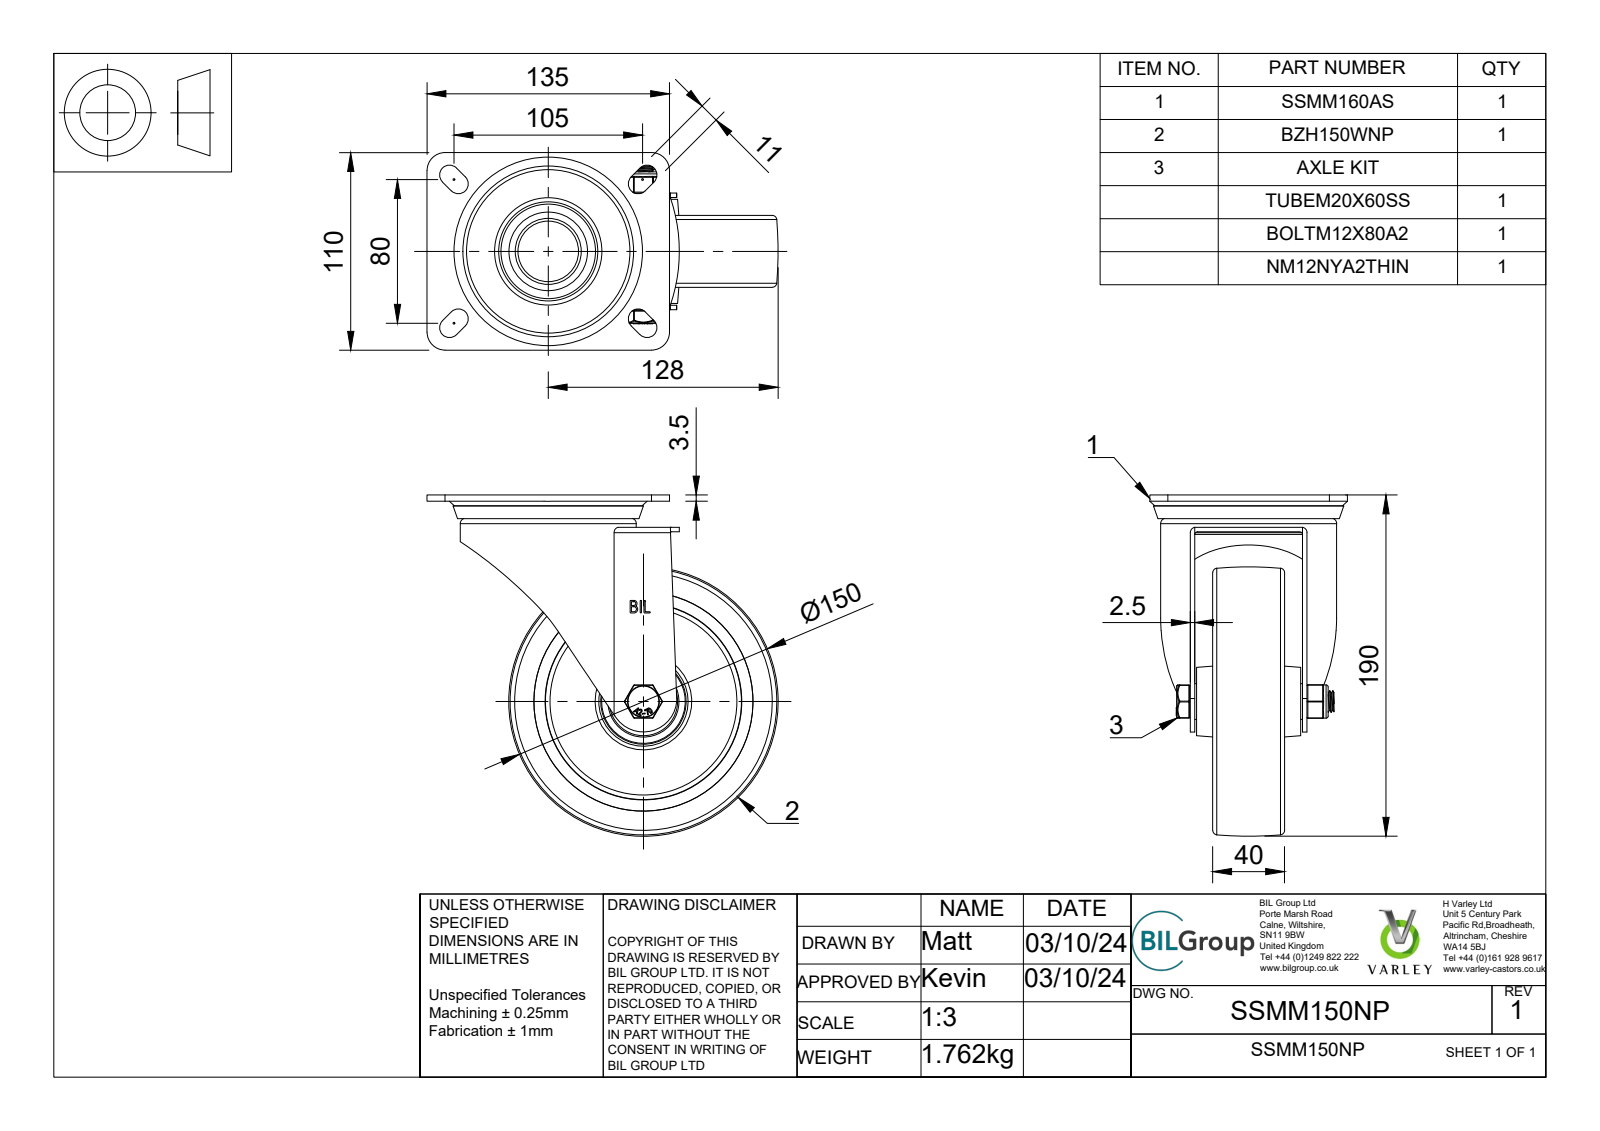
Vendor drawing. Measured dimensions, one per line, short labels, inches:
name: SSMM150NP v4; SSMM160AS v2; ZINC PLATED, PRESSED STEEL TOP PLATE; ZINC PLATED, PRESSED STEEL TOP PLATE Geometry (+7 more)
written by: Autodesk Translation Framework v13.20.0.188 (AUTOMOTIVE_DESIGN)
unit: in
bodies: 49 solids, 414 faces (126 planar, 115 cylindrical, 173 other)
size: 7.697 × 7.48 × 4.331
volume: 38.3 in³; area: 342 in²
holes: 1× ⌀0.472, 1× ⌀0.48, 1× ⌀0.492, 1× ⌀0.551, 1× ⌀0.807, 1× ⌀1.329, 1× ⌀1.565, 1× ⌀3.642, 1× ⌀4.803
bosses: 1× ⌀3.858, 1× ⌀3.071, 1× ⌀1.969, 1× ⌀0.783, 1× ⌀0.728, 1× ⌀0.689, 1× ⌀0.466, 1× ⌀0.387
rounds: 24× R0.02, 8× R0.217, 6× R0.01, 4× R0.059, 4× R0.394, 2× R0.118, 1× R0.732, 1× R3.543
face distances: 0.669, 0.906, 0.492, 0.354, 0.098, 0.394, 1.398, 1.161, 2.067, 0.236
